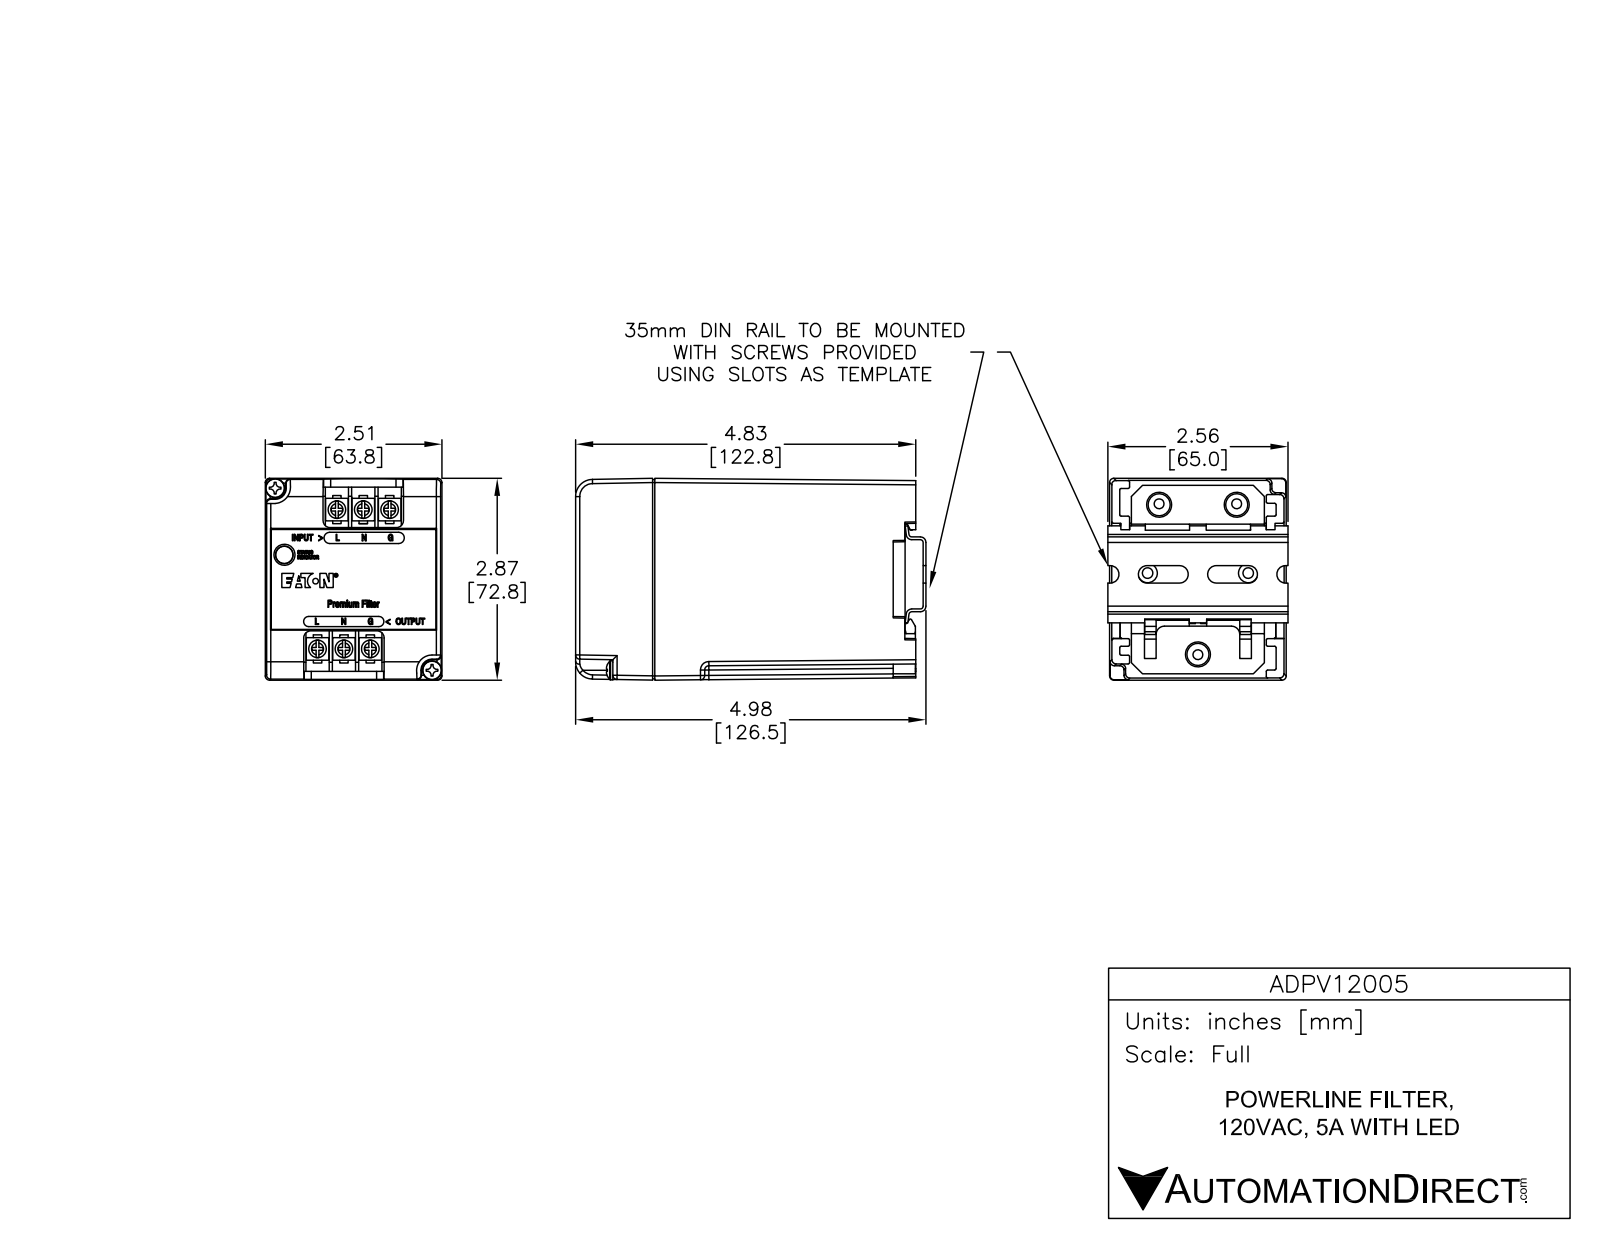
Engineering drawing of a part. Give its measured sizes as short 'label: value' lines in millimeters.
name: AD-PV12005
written by: SolidWorks 2013 (AUTOMOTIVE_DESIGN)
unit: mm
bodies: 27 solids, 654 faces (497 planar, 97 cylindrical, 60 other)
size: 125.3 × 72.8 × 63.7
volume: 527 700 mm³; area: 80 260 mm²
holes: 3× ⌀8, 2× ⌀3.9, 1× ⌀6.3
bosses: 6× ⌀6.4, 6× ⌀1.8, 5× ⌀6, 2× ⌀6.6
rounds: 17× R0.6, 6× R3.1, 4× R1, 4× R2, 4× R6.4, 2× R3.8
face distances: 86.1, 3.8, 114.6, 28.4, 15.4, 108, 111.8, 99.2, 13.1, 5
hole spacings: 56.2, 15.3, 21.4, 24.3, 28, 28.8, 42.6, 43.1
